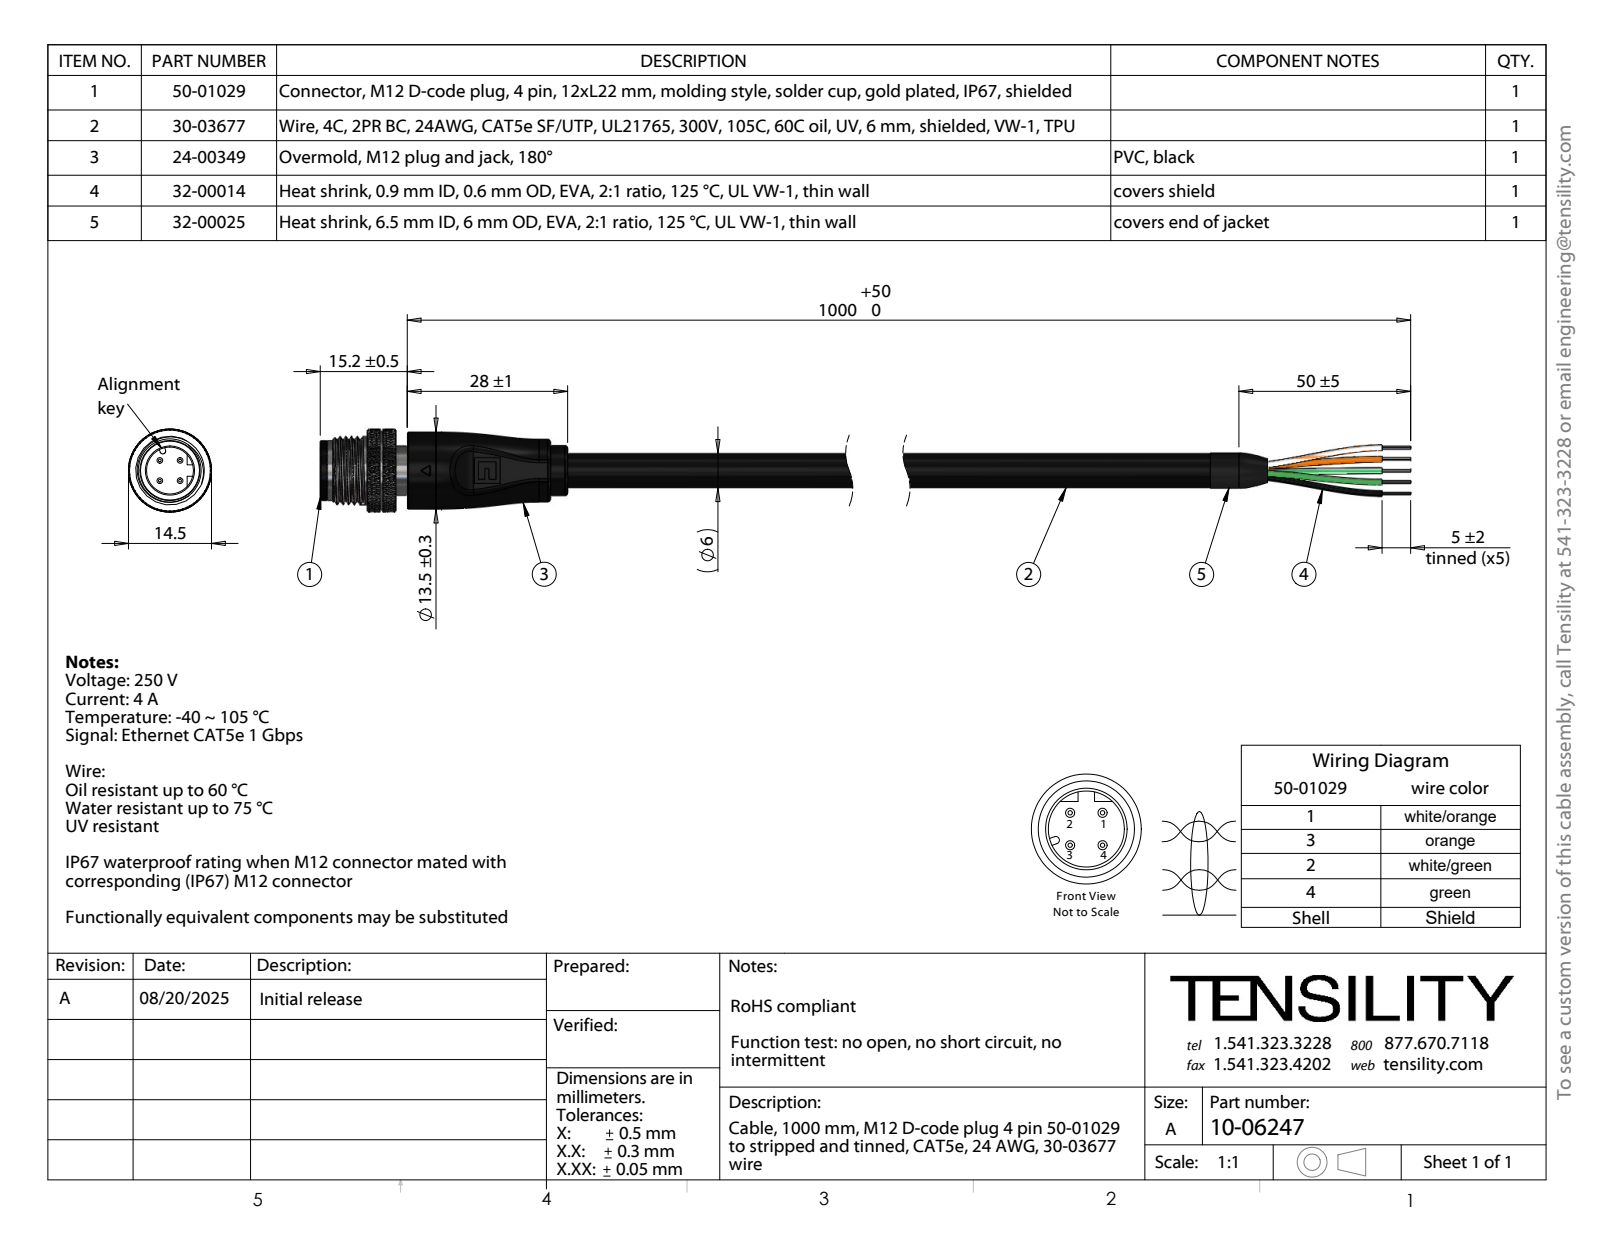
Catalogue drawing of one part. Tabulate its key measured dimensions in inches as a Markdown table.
| quantity | value |
| --- | --- |
| part name | 50-01029_默认; 50-01029-03_默认; 50-01029-04_默认; 30-03677_s + t (+4 more) |
| STEP written by | SolidWorks 2025 (CONFIG_CONTROL_DESIGN) |
| units | inches |
| bodies | 86 solids, 2792 faces (263 planar, 823 cylindrical, 1706 other) |
| overall size | 8.787 × 0.571 × 0.571 |
| volume | 0.567 in³ |
| surface area | 41 in² |
| round holes (diameter × count) | 0.008 × 28, 0.039 × 4, 0.041 × 4, 0.124 × 1, 0.126 × 1, 0.132 × 1, 0.315 × 1, 0.323 × 1, 0.346 × 1, 0.374 × 1 |
| round bosses / shafts (diameter × count) | 0.008 × 35, 0.055 × 4, 0.571 × 1, 0.547 × 1, 0.531 × 1, 0.472 × 1, 0.433 × 1, 0.413 × 1 |
| partial cylindrical surfaces (radius × count) | 0.02 × 2, 0.059 × 2, 0.077 × 2, 0.197 × 1, 0.22 × 1, 0.266 × 1 |
| main face-to-face distances | 7.087, 0.276, 0.079, 7.008, 0.197, 1.102, 1.181, 5.906, 0.425, 0.15 |
| hole center spacings | 0.075, 0.082, 0.042, 0.014, 0.035, 0.043, 0.049, 0.067 |
